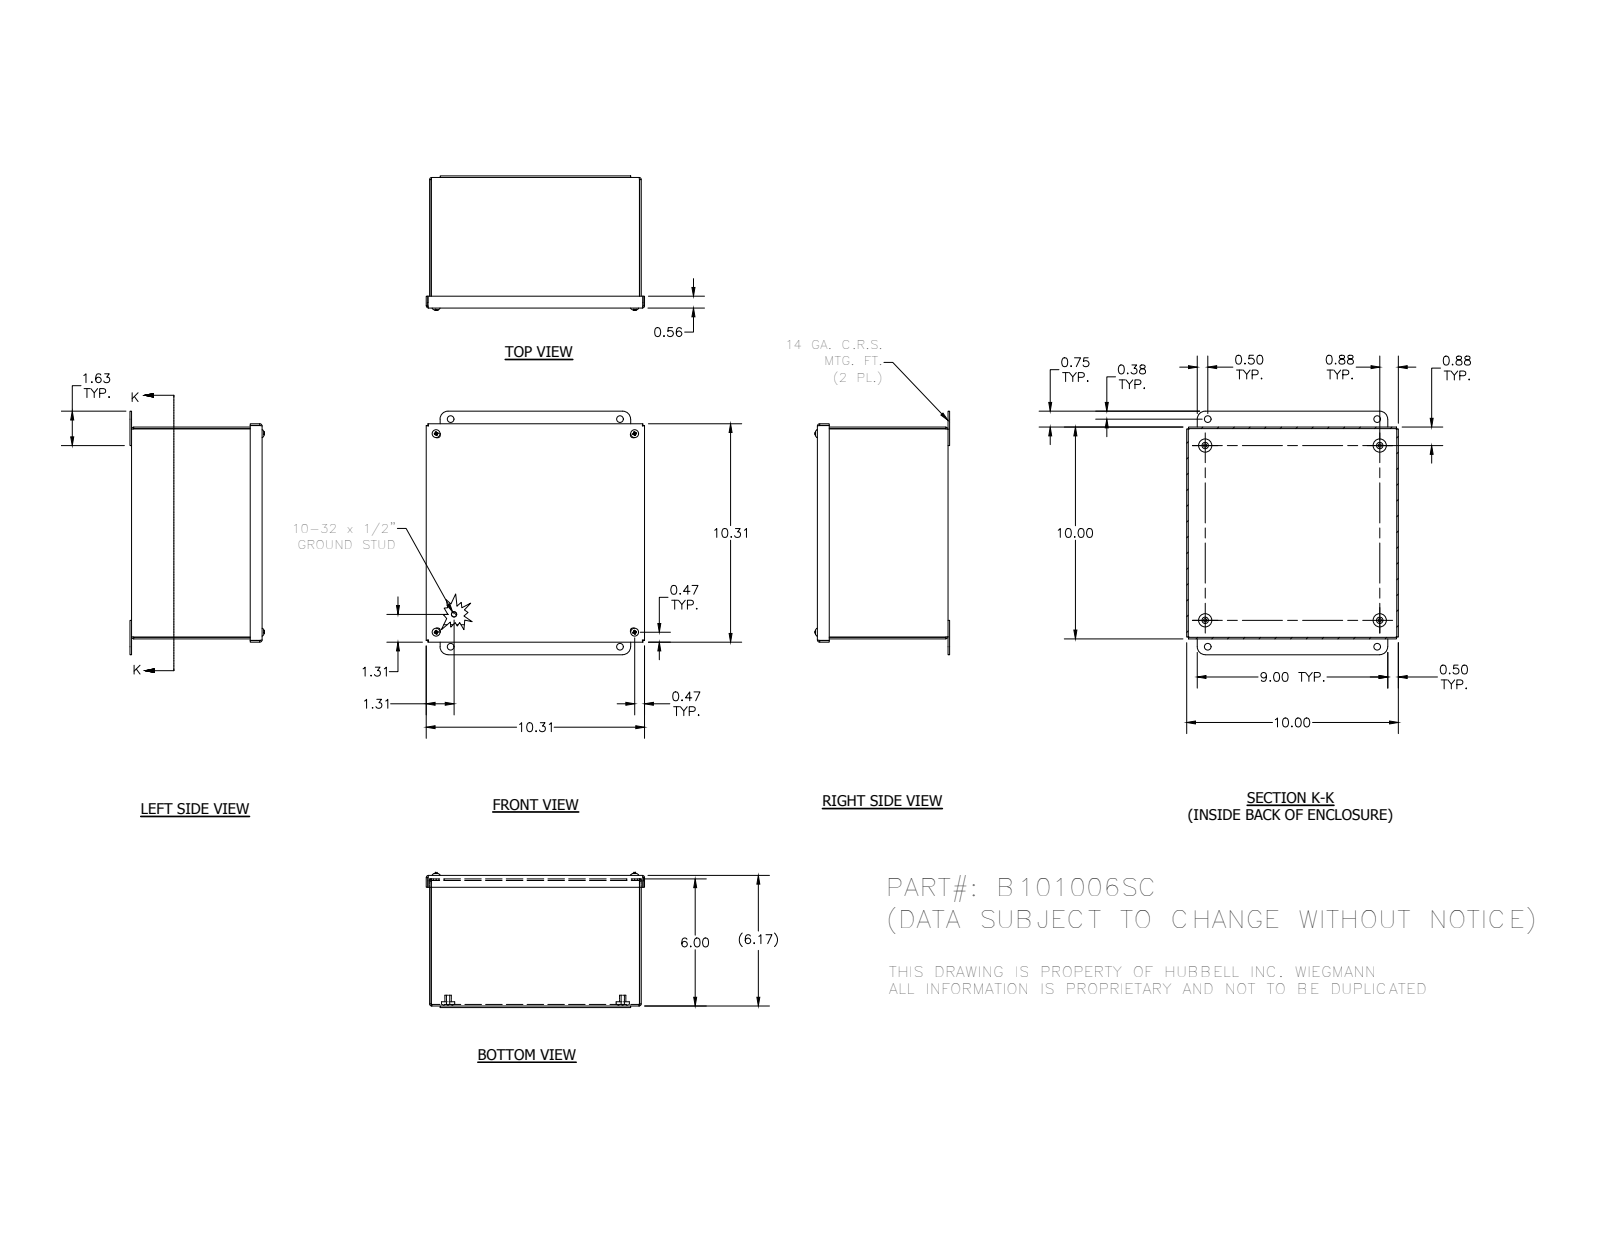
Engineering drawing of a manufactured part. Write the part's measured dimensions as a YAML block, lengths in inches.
part_name: "B101006SC; 3484; 34984; B101006SCBKP (+6 more)"
step_written_by: "Autodesk Inventor 2012 (AUTOMOTIVE_DESIGN)"
units: inches
bodies: {solids: 23, faces: 532, planar: 311, cylindrical: 102, other: 119}
overall_size: [11.5, 10.313, 6.346]
volume: 42.26
surface_area: 1087
round_holes:
  - {diameter: 0.145, count: 4}
  - {diameter: 0.156, count: 4}
  - {diameter: 0.196, count: 4}
  - {diameter: 0.278, count: 4}
  - {diameter: 0.281, count: 4}
  - {diameter: 0.31, count: 4}
  - {diameter: 0.313, count: 4}
round_bosses_or_shafts:
  - {diameter: 0.19, count: 5}
  - {diameter: 0.625, count: 4}
  - {diameter: 0.453, count: 4}
  - {diameter: 0.406, count: 4}
  - {diameter: 0.373, count: 4}
  - {diameter: 0.3, count: 4}
  - {diameter: 0.248, count: 4}
  - {diameter: 0.25, count: 1}
partial_cylinders:
  - {radius: 0.031, count: 12}
  - {radius: 0.105, count: 12}
  - {radius: 0.089, count: 4}
  - {radius: 0.375, count: 4}
face_to_face_distances: [0.074, 9.926, 6.094, 10, 9.852, 6.168, 6.02, 0.075, 0.149, 6.169]
hole_center_spacings: [9.314, 8.83, 9.374, 9.375, 8.714, 9.395, 13.172, 0.087]
